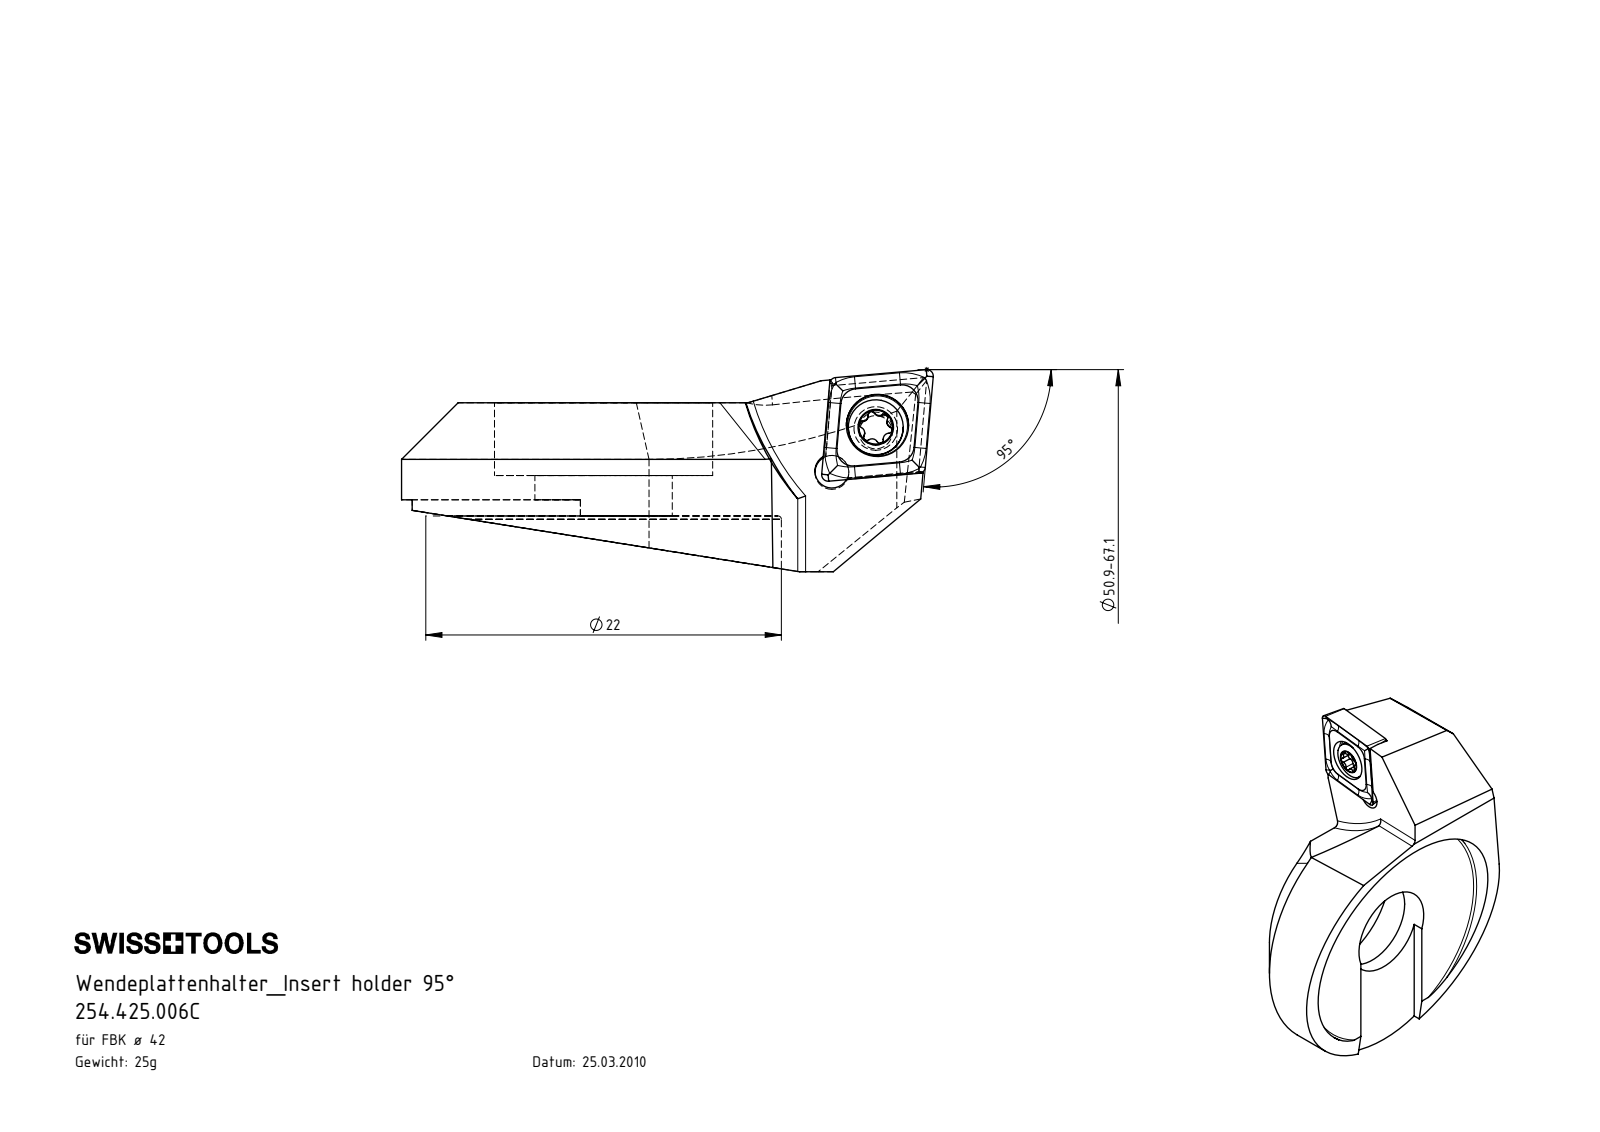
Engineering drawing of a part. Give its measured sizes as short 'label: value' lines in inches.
name: 254.425.006C; WCA-ER2.001.006_A; CCMT060204; F42-WCA.002.009_C_fertigbearbeitet
written by: SolidWorks 2017 (CONFIG_CONTROL_DESIGN)
unit: in
bodies: 5 solids, 147 faces (48 planar, 45 cylindrical, 54 other)
size: 1.295 × 0.984 × 0.492
volume: 0.197 in³; area: 4.222 in²
holes: 1× ⌀0.081, 1× ⌀0.083, 1× ⌀0.11, 1× ⌀0.152, 1× ⌀0.335, 1× ⌀0.531
bosses: 1× ⌀0.134, 1× ⌀0.098
rounds: 6× R0.008, 5× R0.014, 2× R0.02, 1× R0.014, 1× R0.041, 1× R0.197, 1× R0.433, 1× R0.492
face distances: 0.276, 0.264, 0.177, 0.165, 0.098, 0.09, 0.236, 0.224, 0.059, 0.039
hole spacings: 0.151, 0.157
